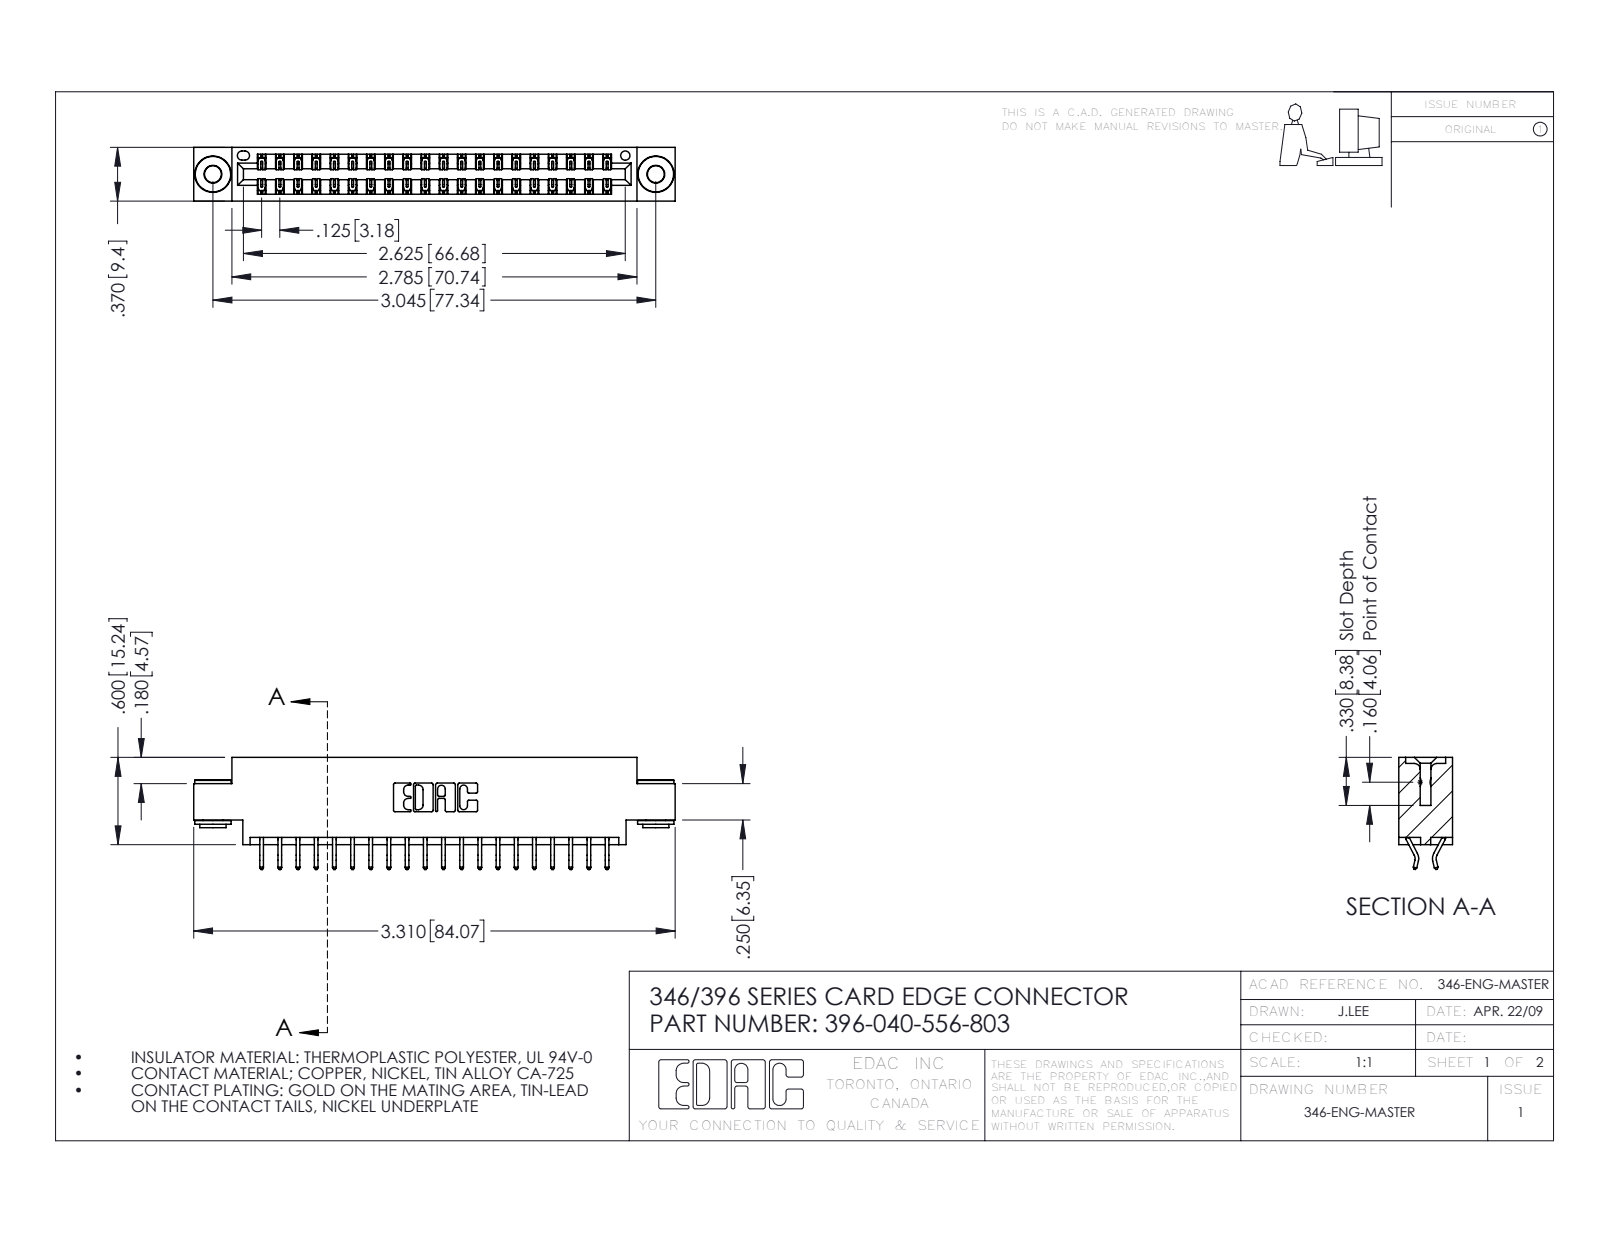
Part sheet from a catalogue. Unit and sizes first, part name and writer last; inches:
Units: inches
Overall size (bounding box): 3.31 × 0.77 × 0.37
Round holes (diameter × count): ⌀0.116 ×2, ⌀0.156 ×2, ⌀0.064 ×1
Round bosses / shafts (diameter × count): ⌀0.25 ×2, ⌀0.18 ×2, ⌀0.136 ×2
Partial cylindrical surfaces — rounded edges, fillets, slot ends (radius × count): R0.006 ×60, R0.01 ×22, R0.007 ×6, R0.031 ×6, R0.026 ×3, R0.01 ×2, R0.014 ×2, R0.022 ×2
Main face-to-face distances: 0.048, 0.322, 0.37, 0.25, 0.025, 0.275, 0.072, 0.298, 0.148, 0.222
Hole centre spacings: 0.246, 2.837, 3.045
Volume: 0.482 in³ · Surface area: 16.83 in²
Bodies: 43 solids, 2484 faces (1650 planar, 826 cylindrical, 8 other)
Part name (STEP PRODUCT): 346 Part_0.170 Offset - 0.156 Dia-TH; 345-250-002_345-250-002-102; 396-040-556-803; 345-292-001_556 Tail
STEP written by: SolidWorks 2016 (CONFIG_CONTROL_DESIGN)
